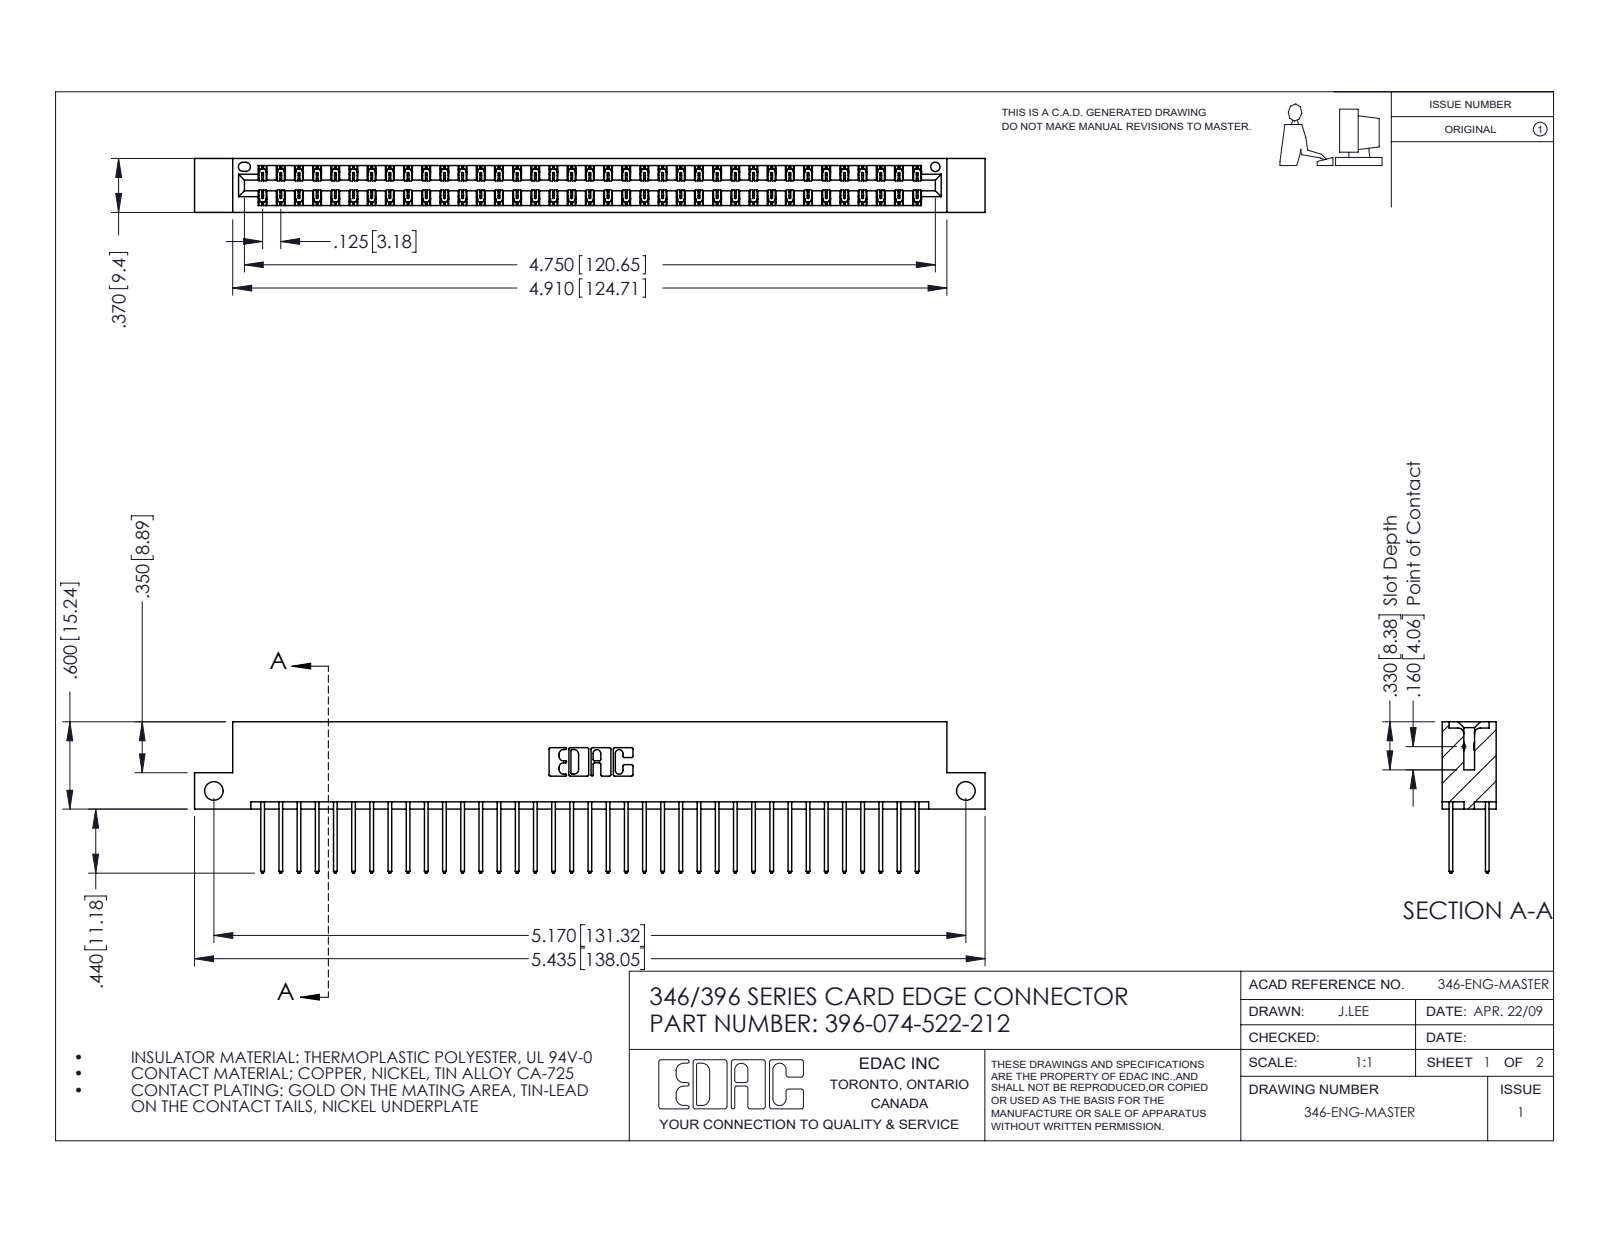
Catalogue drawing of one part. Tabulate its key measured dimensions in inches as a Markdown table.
| quantity | value |
| --- | --- |
| part name | 345-292-001_345-293-122; 346 Part_Flush Mounting Lugs - Side Mount; 396-074-522-212 |
| STEP written by | SolidWorks 2016 (CONFIG_CONTROL_DESIGN) |
| units | inches |
| bodies | 75 solids, 3970 faces (2666 planar, 1304 cylindrical, 0 other) |
| overall size | 5.435 × 1.04 × 0.37 |
| volume | 0.825 in³ |
| surface area | 29.84 in² |
| round holes (diameter × count) | 0.128 × 2, 0.064 × 1 |
| partial cylindrical surfaces (radius × count) | 0.006 × 111, 0.01 × 74, 0.01 × 22, 0.007 × 6, 0.031 × 6, 0.026 × 3, 0.014 × 2, 0.022 × 2 |
| main face-to-face distances | 0.048, 0.322, 0.25, 0.37, 0.072, 0.298, 0.025, 0.275, 0.148, 0.222 |
| hole center spacings | 5.17 |
